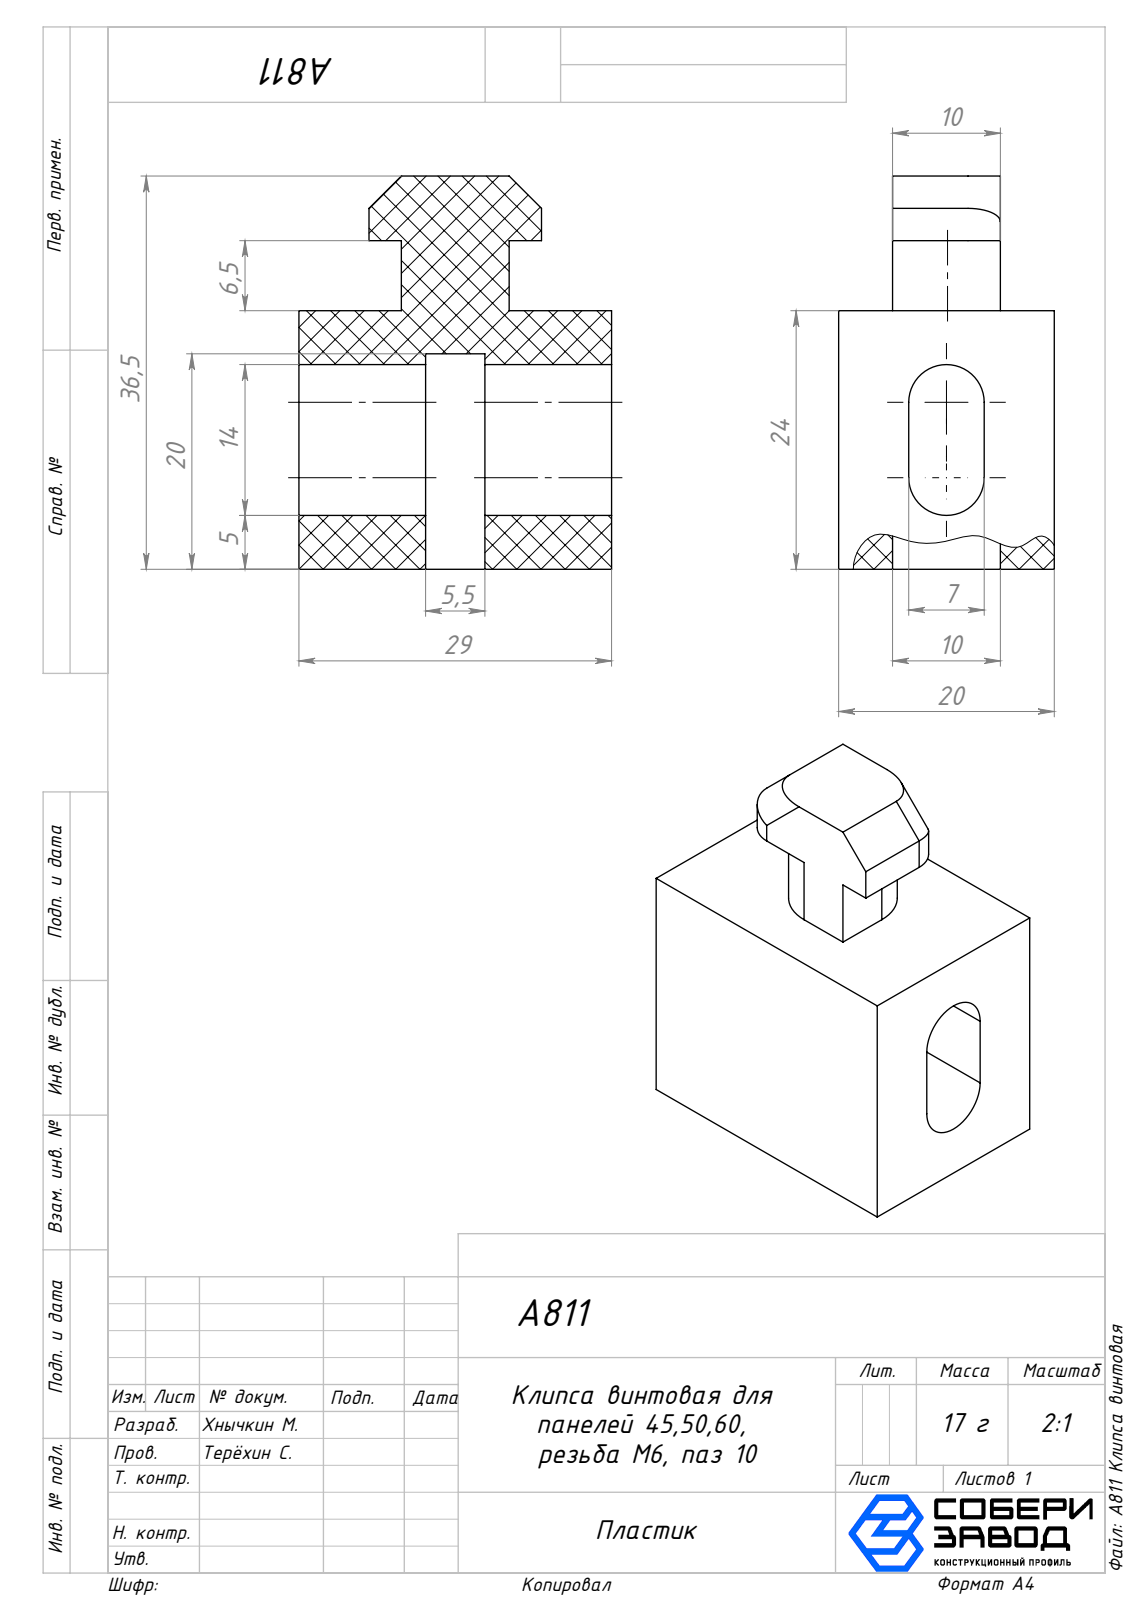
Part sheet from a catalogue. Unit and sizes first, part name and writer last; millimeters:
Units: millimetres
Overall size (bounding box): 36.5 × 29 × 20
Partial cylindrical surfaces — rounded edges, fillets, slot ends (radius × count): R3 ×4, R3.5 ×2, R4.9 ×2
Main face-to-face distances: 20, 24, 6.5, 5, 15, 29, 13.5, 1.5, 8.5, 10
Volume: 12 189 mm³ · Surface area: 5 232 mm²
Bodies: 1 solid, 36 faces (26 planar, 10 cylindrical, 0 other)
Part name (STEP PRODUCT): A811 Клипса винтовая
STEP written by: SolidWorks 2025 (AUTOMOTIVE_DESIGN)
